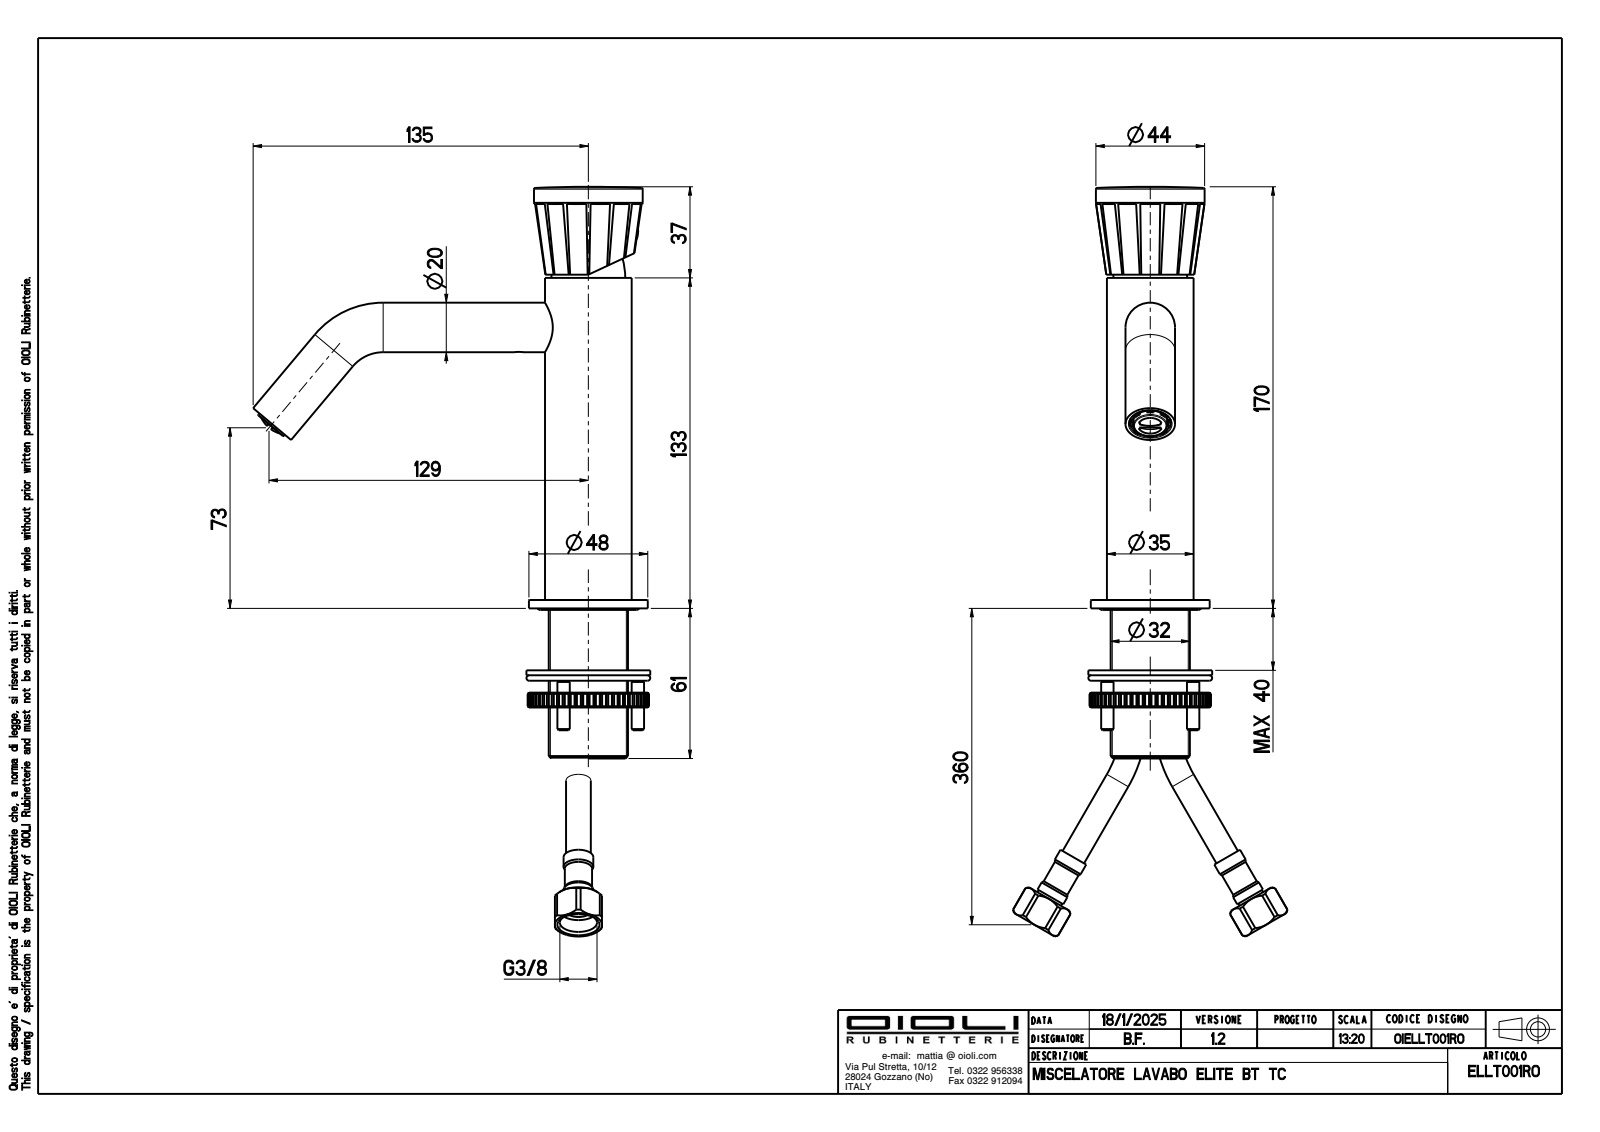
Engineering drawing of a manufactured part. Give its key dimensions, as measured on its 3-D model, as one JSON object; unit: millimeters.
{"part_name": "OIBR00322; OIBR00605; OICT00087; OIVT00002 (+6 more)", "step_written_by": "CREO PARAMETRIC BY PTC INC, 2024493 (CONFIG_CONTROL_DESIGN)", "units": "millimeters", "bodies": {"solids": 10, "faces": 985, "planar": 571, "cylindrical": 184, "other": 230}, "overall_size": [170.18, 159.37, 48], "volume_mm3": 90905, "surface_area_mm2": 62604, "round_holes": [[3.2, 2], [5, 2], [7, 2], [9, 2], [15, 2], [15.5, 2], [3.3, 1], [4, 1], [4.2, 1], [5.3, 1], [6.5, 1], [9.5, 1]], "round_bosses_or_shafts": [[16.5, 3], [20, 2], [8, 2], [48, 1], [43.9, 1], [35.6, 1], [35, 1], [32, 1]], "partial_cylinders_radius": [[0.1, 14], [0.9, 8], [0.6, 4], [0.45, 3], [2.5, 1], [6.72, 1], [7.46, 1], [8.5, 1]], "face_to_face_distances": [163.8, 3.4, 167.2, 83.4, 80, 83.8, 133.4, 130, 50, 33.8], "hole_center_spacings": [1.9, 6.72, 7.63, 8.14, 8.94, 9.33, 11.27, 15.46]}
